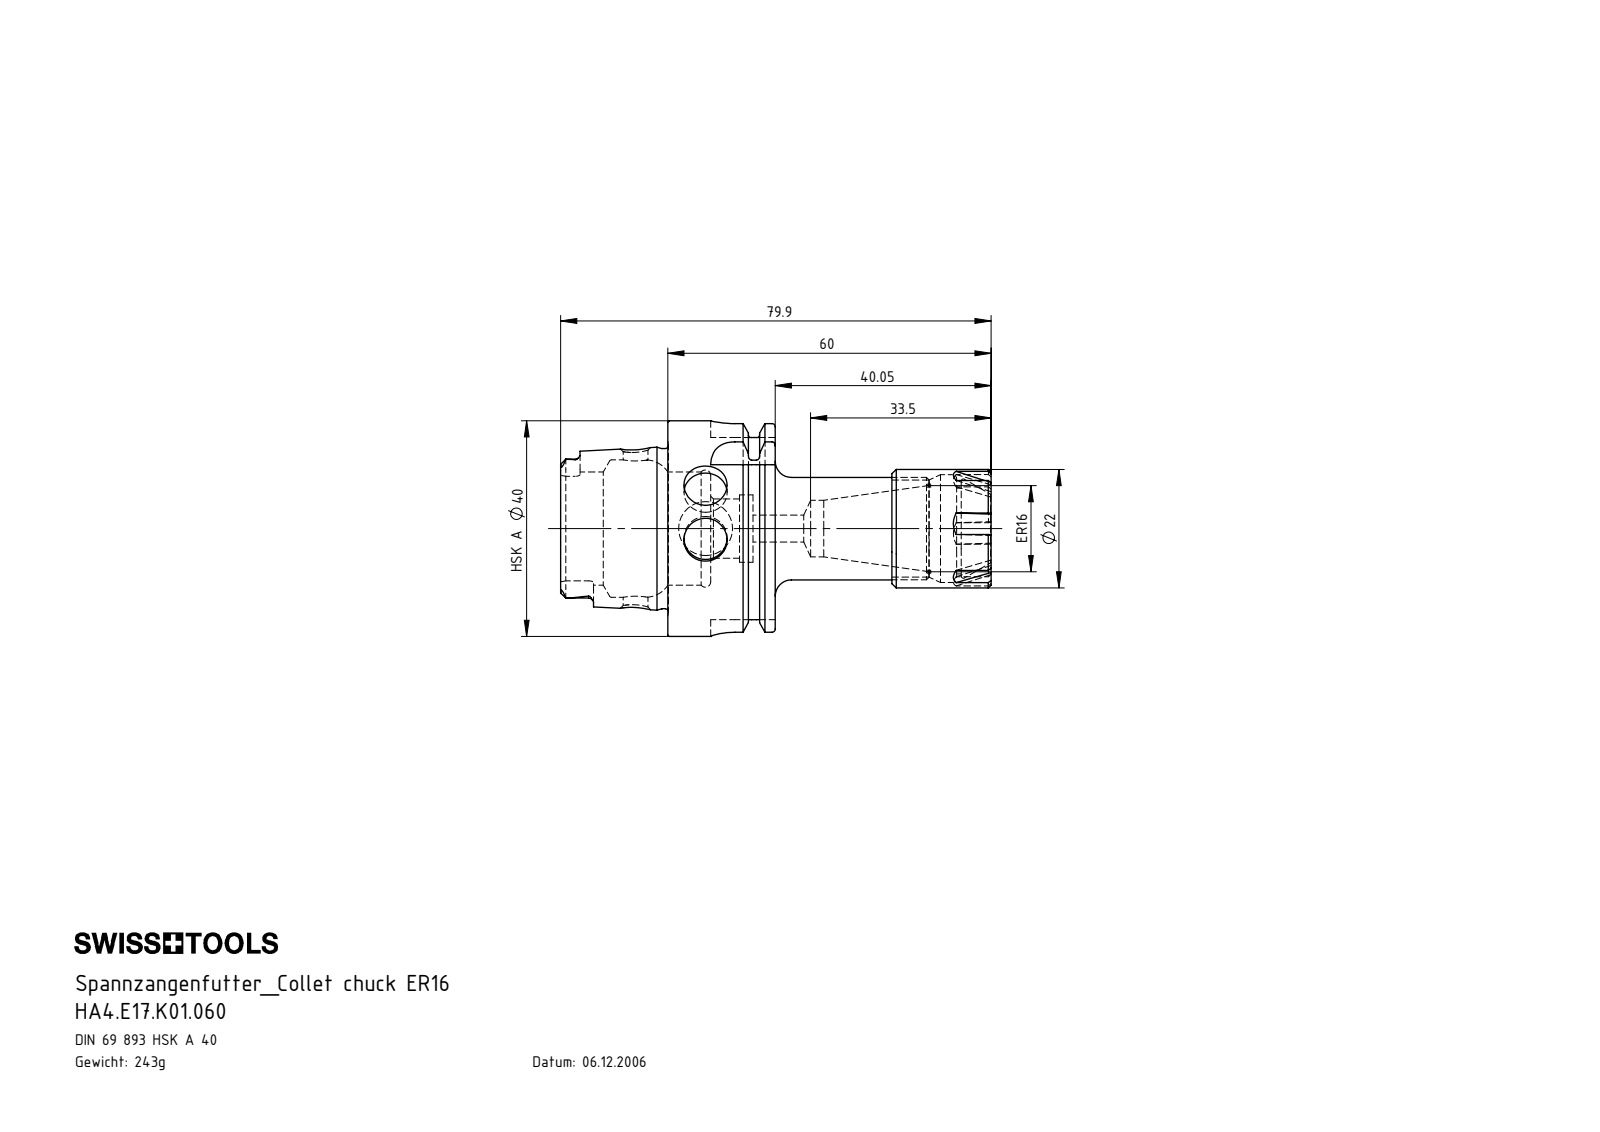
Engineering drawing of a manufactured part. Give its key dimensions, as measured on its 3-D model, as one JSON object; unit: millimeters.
{"part_name": "HA4-E17.K01.060_B_Fertigbearbeitung; HA4.E17.K01.060; E17-ER1.001.018", "step_written_by": "SolidWorks 2017 (CONFIG_CONTROL_DESIGN)", "units": "millimeters", "bodies": {"solids": 2, "faces": 219, "planar": 70, "cylindrical": 63, "other": 86}, "overall_size": [79.9, 40, 40], "volume_mm3": 31168, "surface_area_mm2": 14994, "round_holes": [[8, 2], [4.6, 1], [5, 1], [10, 1], [10.5, 1], [11, 1], [12.5, 1], [12.7, 1], [18, 1], [20, 1], [21, 1], [25.5, 1]], "round_bosses_or_shafts": [[40, 1], [34.75, 1], [29.71, 1], [22, 1], [19, 1]], "partial_cylinders_radius": [[0.9, 6], [1.88, 4], [4.5, 4], [7.7, 2]], "face_to_face_distances": [19.95, 12, 7.95, 60, 52.05, 40.05, 33.65, 19.9, 27.85, 39.85]}
